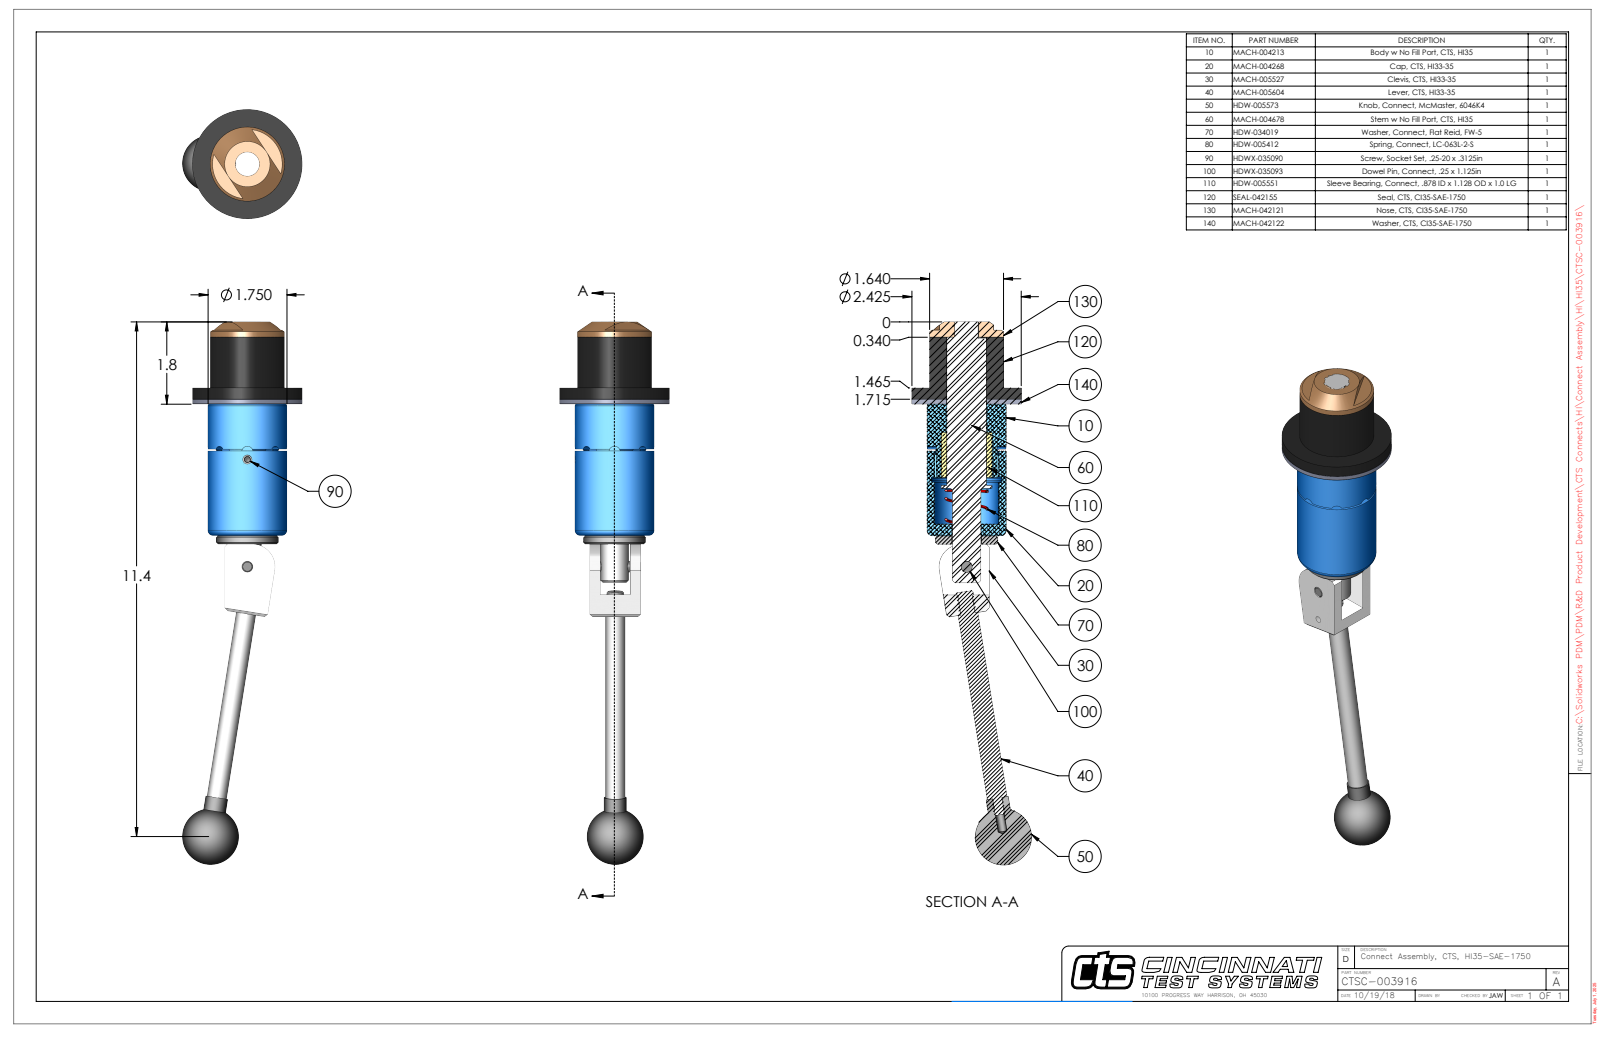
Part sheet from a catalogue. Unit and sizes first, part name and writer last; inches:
Units: inches
Overall size (bounding box): 12.039 × 2.65 × 2.425
Round holes (diameter × count): ⌀0.201 ×2, ⌀0.15 ×1, ⌀0.249 ×1, ⌀0.251 ×1, ⌀0.313 ×1, ⌀0.531 ×1, ⌀0.635 ×1, ⌀0.656 ×1, ⌀0.876 ×1, ⌀0.883 ×1, ⌀0.885 ×1, ⌀1.419 ×1
Round bosses / shafts (diameter × count): ⌀0.25 ×2, ⌀2.425 ×1, ⌀1.75 ×1, ⌀1.64 ×1, ⌀1.38 ×1, ⌀0.871 ×1, ⌀0.869 ×1, ⌀0.625 ×1
Partial cylindrical surfaces — rounded edges, fillets, slot ends (radius × count): R0.125 ×4, R0.029 ×2, R0.5 ×1, R0.695 ×1, R0.822 ×1
Main face-to-face distances: 0.11, 1.375, 1.485, 1.125, 0.25, 0.36, 4.402, 3.277, 3.027, 2.917
Hole centre spacings: 0.74, 2.376, 3.116
Volume: 14.77 in³ · Surface area: 92.62 in²
Bodies: 10 solids, 249 faces (91 planar, 100 cylindrical, 58 other)
Part name (STEP PRODUCT): CTSC-003916
STEP written by: SolidWorks 2023 (AUTOMOTIVE_DESIGN)
